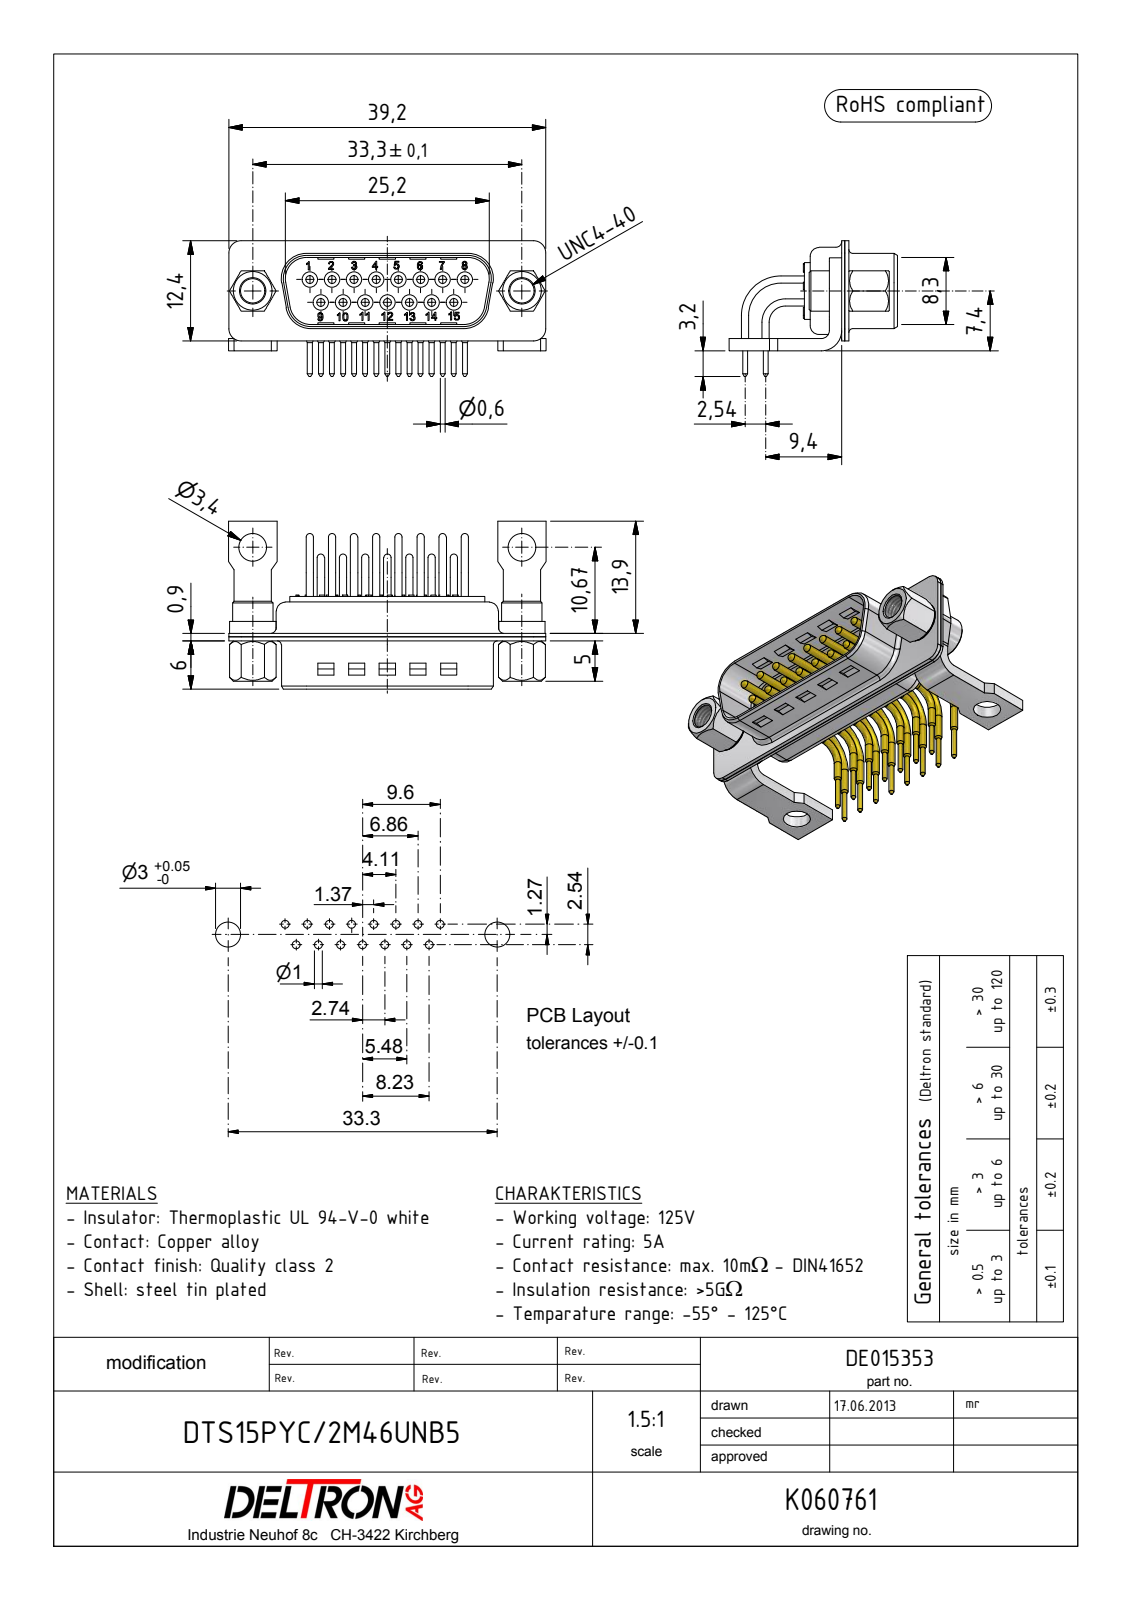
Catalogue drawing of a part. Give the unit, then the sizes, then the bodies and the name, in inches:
Units: inches
Overall size (bounding box): 1.547 × 0.819 × 0.661
Round holes (diameter × count): ⌀0.076 ×15, ⌀0.091 ×15, ⌀0.013 ×2, ⌀0.118 ×2, ⌀0.126 ×2, ⌀0.134 ×2, ⌀0.159 ×2, ⌀0.16 ×2, ⌀0.009 ×1, ⌀0.011 ×1
Round bosses / shafts (diameter × count): ⌀0.035 ×30, ⌀0.077 ×15, ⌀0.076 ×15, ⌀0.063 ×15, ⌀0.063 ×15, ⌀0.039 ×15, ⌀0.024 ×15, ⌀0.197 ×2
Partial cylindrical surfaces — rounded edges, fillets, slot ends (radius × count): R0.079 ×20, R0.042 ×15, R0.039 ×9, R0.01 ×8, R0.02 ×8, R0.028 ×8, R0.043 ×8, R0.047 ×4
Main face-to-face distances: 0.02, 0.016, 0.035, 0.059, 0.026, 0.197, 0.396, 0.049, 0.094, 0.346
Hole centre spacings: 0.124, 0.108, 0.197, 0.216, 0.292, 0.324, 0.394, 0.431
Volume: 0.14 in³ · Surface area: 9.791 in²
Bodies: 24 solids, 2837 faces (1684 planar, 838 cylindrical, 315 other)
Part name (STEP PRODUCT): N00403_BG; R+B00913_BG; R+B00914_BG; R+B00153_BG (+5 more)
STEP written by: Autodesk Inventor 2015 (AUTOMOTIVE_DESIGN)
